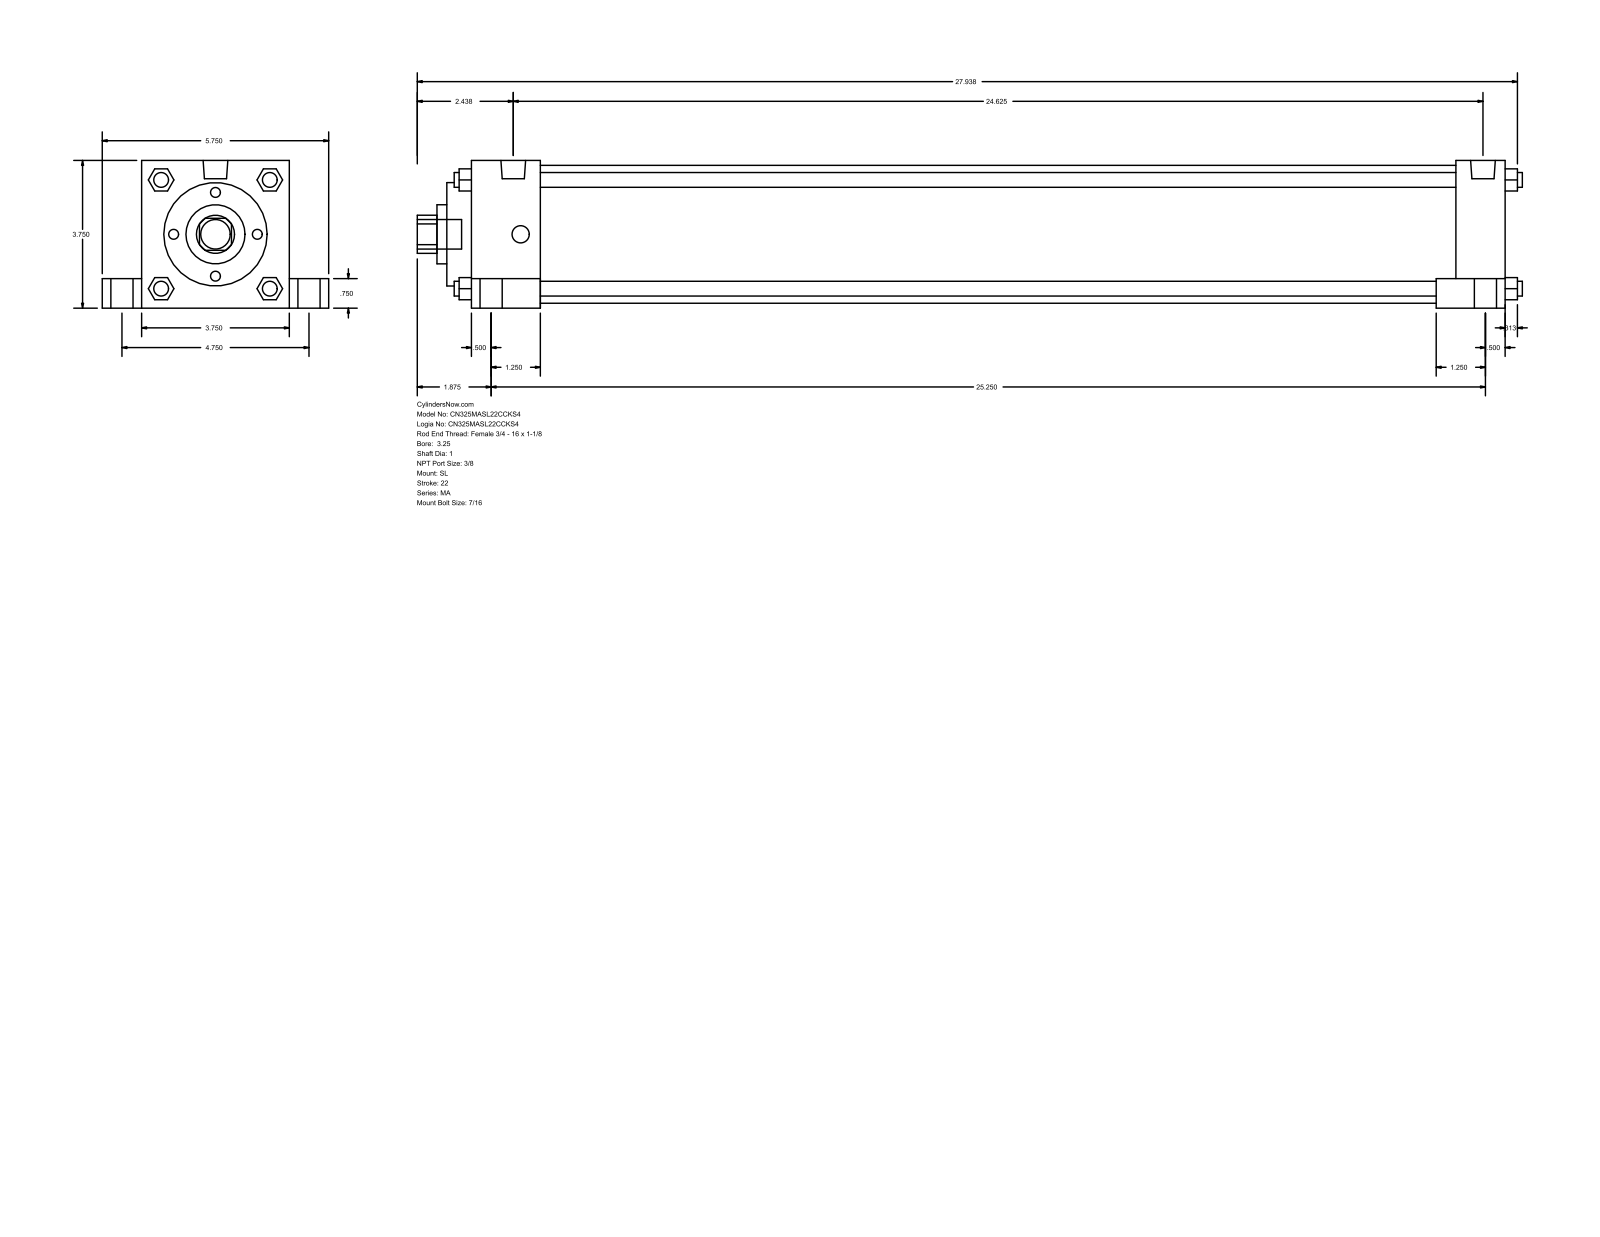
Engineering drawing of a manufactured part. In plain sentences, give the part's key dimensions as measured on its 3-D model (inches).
The part is named "MA_SL__0325_1". Its 3-D file was written by "GSSL Pune (CONFIG_CONTROL_DESIGN)". It is 0 solids with 150 faces: 113 planar, 37 cylindrical and 0 other. Overall it measures 28.063 by 5.75 by 3.75 inches. Round holes: 1 of diameter 1, 1 of diameter 1.5, 1 of diameter 2.625, 1 of diameter 3.5. Round bosses or shafts: 4 of diameter 0.813, 4 of diameter 0.563, 4 of diameter 0.437, 4 of diameter 0.375, 2 of diameter 0.627, 1 of diameter 0.75. Partial cylindrical surfaces (rounded edges, fillets, slot ends): 1 of radius 0.484. The main face-to-face distances are 3.75, 26.25, 0.625, 1, 4.75, 26.875, 0.75, 25, 1.25, 1.75.
